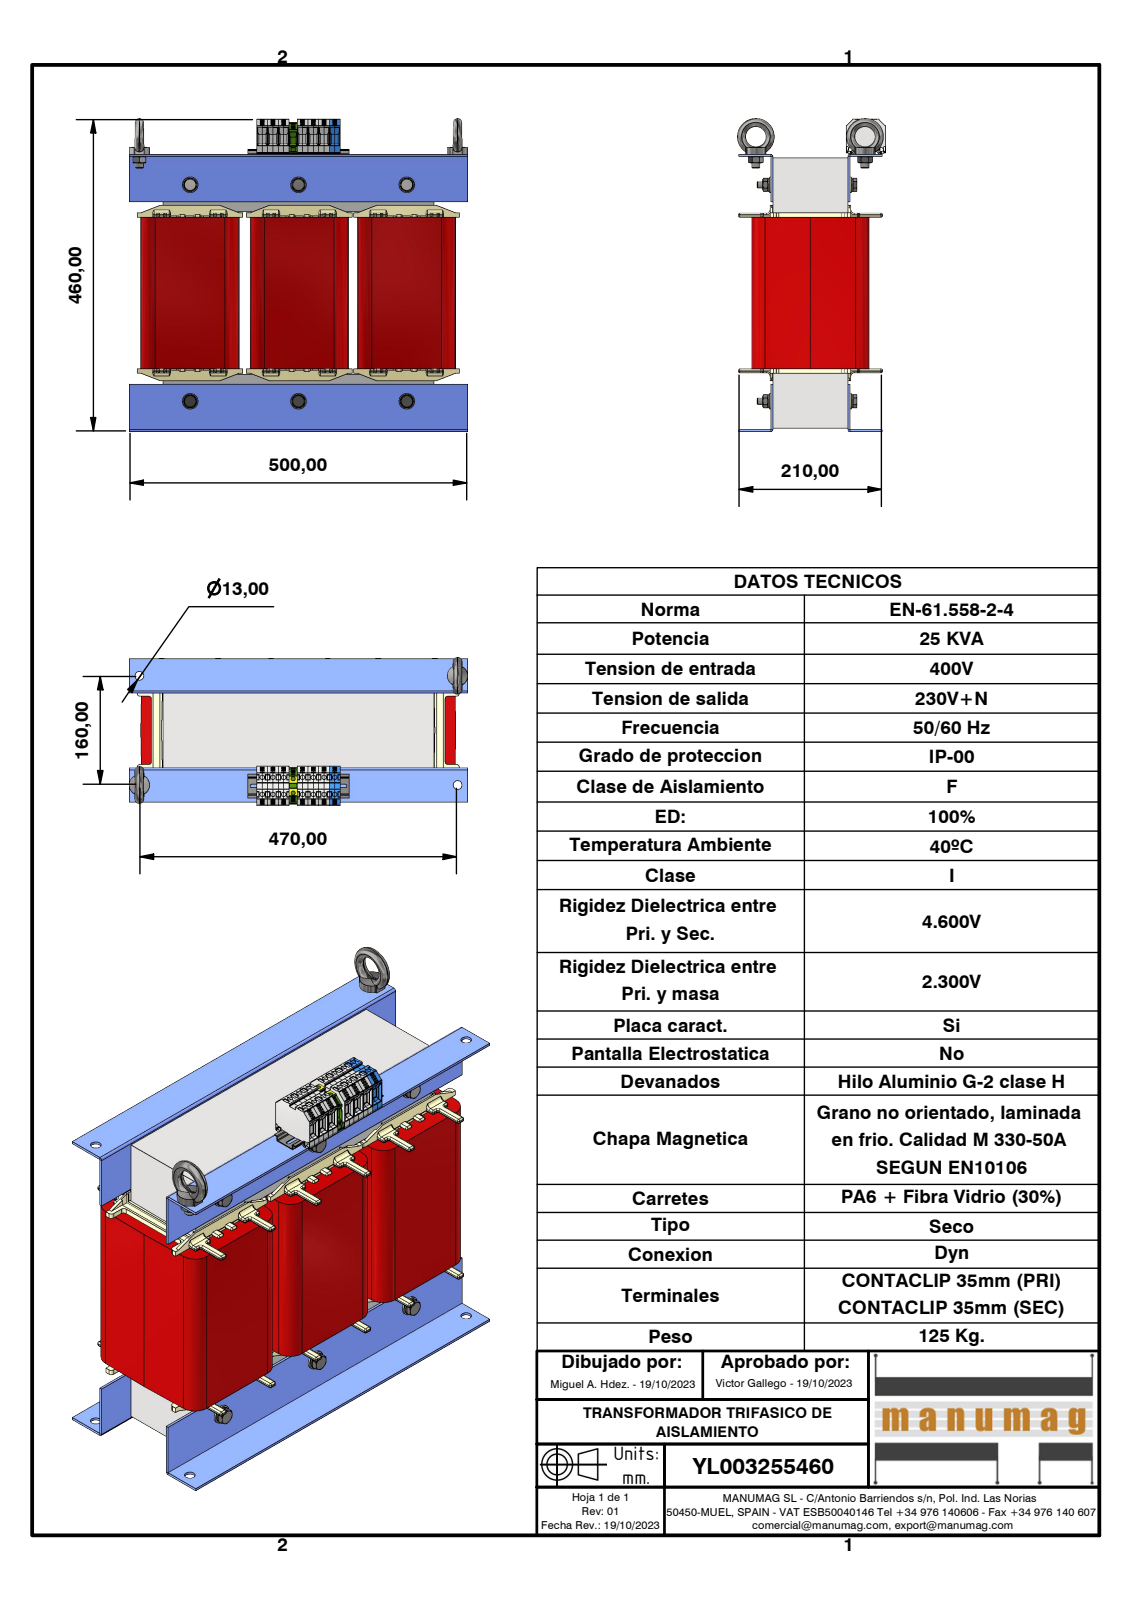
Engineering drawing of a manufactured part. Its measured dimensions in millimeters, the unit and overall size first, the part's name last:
Units: millimetres
Overall size (bounding box): 500 × 463 × 217.3
Round holes (diameter × count): ⌀6.5 ×14, ⌀13 ×10, ⌀8.38 ×6, ⌀10 ×6, ⌀10.5 ×6, ⌀15 ×6, ⌀2 ×4, ⌀6.3 ×2, ⌀10.11 ×2, ⌀30 ×2
Round bosses / shafts (diameter × count): ⌀0.6 ×12, ⌀23 ×6, ⌀20 ×6, ⌀15.4 ×6, ⌀11.5 ×6, ⌀9.19 ×6, ⌀54 ×2, ⌀12 ×2
Partial cylindrical surfaces — rounded edges, fillets, slot ends (radius × count): R0.3 ×494, R2 ×202, R0.5 ×188, R1 ×90, R0.25 ×34, R0.81 ×33, R1.9 ×32, R4 ×26
Main face-to-face distances: 3, 320, 110, 6, 30.86, 113, 116, 2, 116.2, 24.85
Hole centre spacings: 15.9, 29.63, 25, 160, 31.8, 40.45, 59.6, 64.63
Volume: 24 370 000 mm³ · Surface area: 2 676 000 mm²
Bodies: 57 solids, 8917 faces (4885 planar, 2650 cylindrical, 1382 other)
Part name (STEP PRODUCT): YL003255460; 3UI240 400 x 400 - 110; UI 240_110_BOBINADO; RC80 NT080 (+8 more)
STEP written by: Autodesk Inventor 2023 (AUTOMOTIVE_DESIGN)
